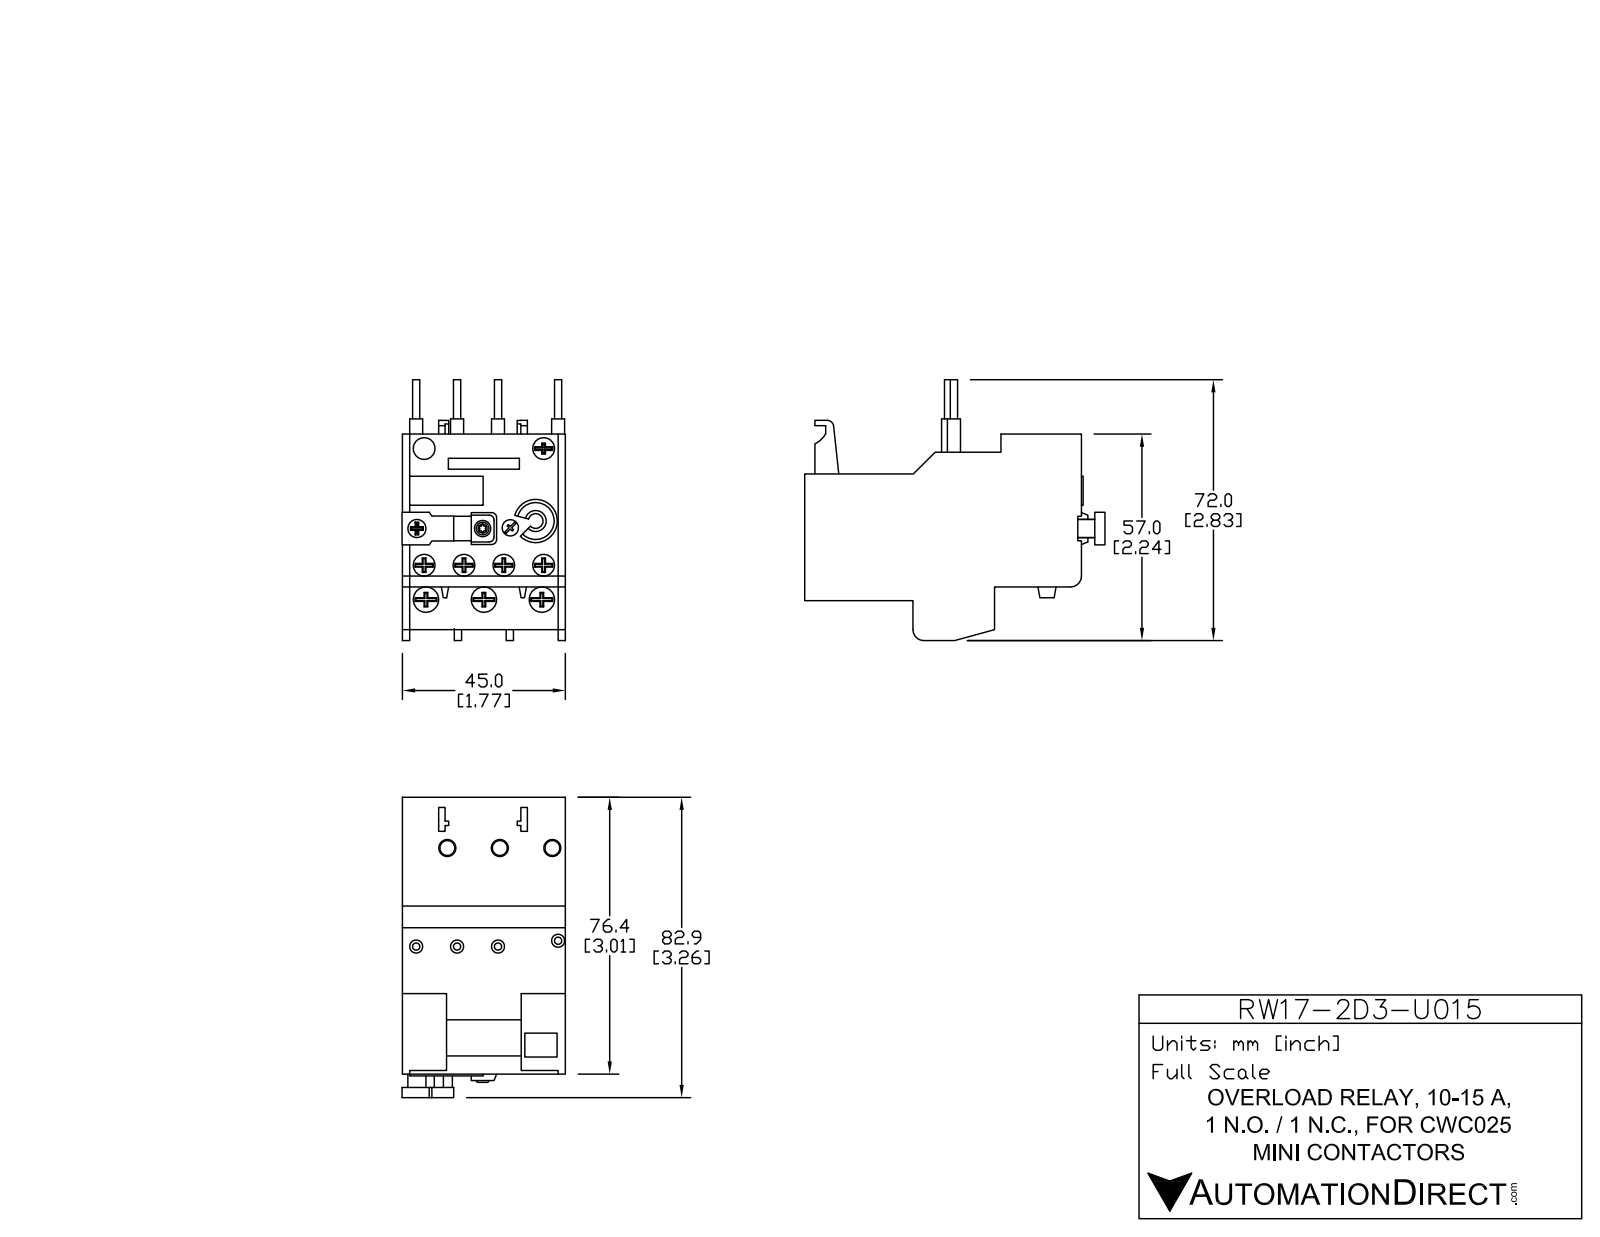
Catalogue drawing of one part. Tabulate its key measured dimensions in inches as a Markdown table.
| quantity | value |
| --- | --- |
| part name | RW17D-2D3-U015 |
| STEP written by | SolidWorks 2013 (AUTOMOTIVE_DESIGN) |
| units | inches |
| bodies | 17 solids, 748 faces (512 planar, 211 cylindrical, 25 other) |
| overall size | 3.254 × 2.776 × 1.793 |
| volume | 7.772 in³ |
| surface area | 53.57 in² |
| round holes (diameter × count) | 0.236 × 6, 0.157 × 3, 0.276 × 3, 0.295 × 3, 0.177 × 1, 0.187 × 1, 0.21 × 1, 0.217 × 1, 0.41 × 1 |
| round bosses / shafts (diameter × count) | 0.217 × 7, 0.118 × 7, 0.069 × 4, 0.22 × 2, 0.128 × 2, 0.253 × 1, 0.242 × 1, 0.187 × 1 |
| partial cylindrical surfaces (radius × count) | 0.02 × 20, 0.01 × 12, 0.039 × 9, 0.178 × 6, 0.231 × 4, 0.309 × 4, 0.059 × 3, 0.049 × 2 |
| main face-to-face distances | 1.791, 0.059, 0.427, 0.433, 3.008, 1.378, 0.056, 2.952, 2.949, 0.236 |
| hole center spacings | 0.591, 0.337, 0.423, 1.181, 0.416, 0.467, 0.561, 0.841 |
